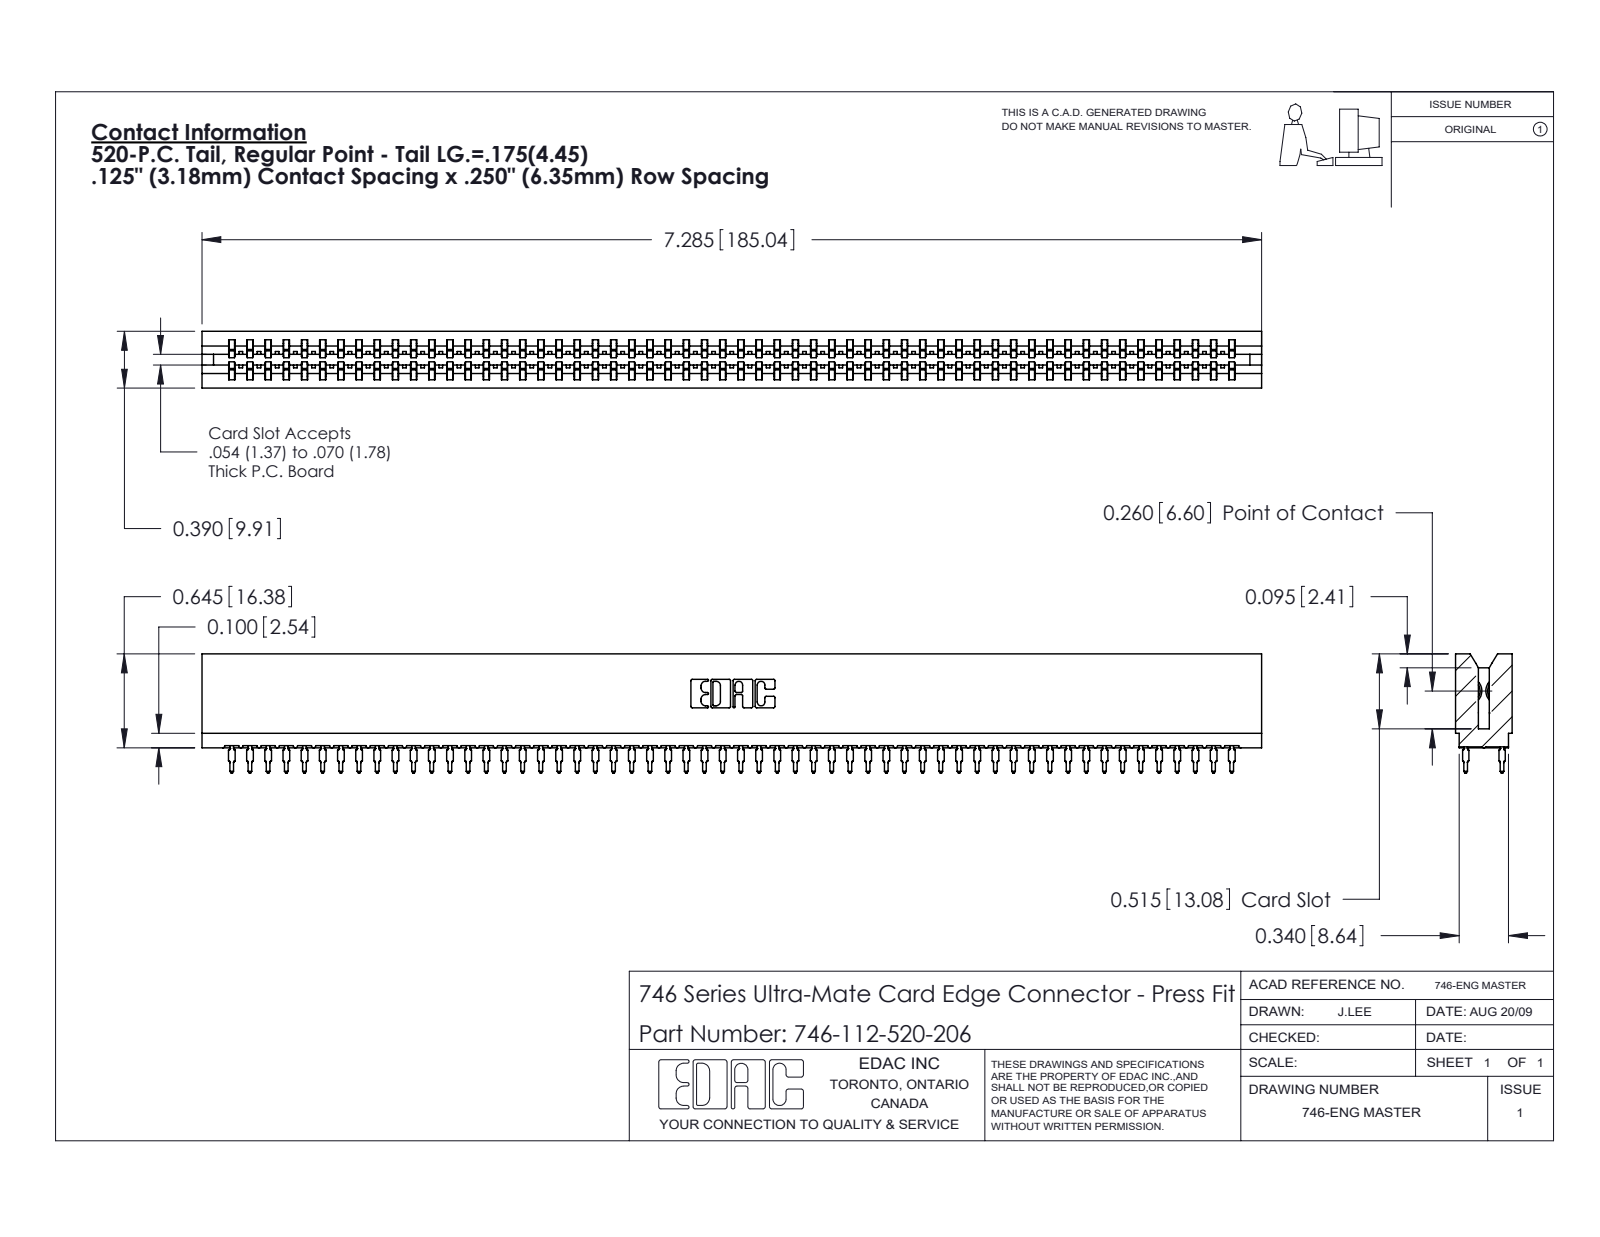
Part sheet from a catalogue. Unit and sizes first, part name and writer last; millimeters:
Units: millimetres
Overall size (bounding box): 185 × 20.8 × 9.9
Partial cylindrical surfaces — rounded edges, fillets, slot ends (radius × count): R0.5 ×224, R0.4 ×57, R0.3 ×22, R0.1 ×8, R0.3 ×8, R0.2 ×6, R0.8 ×6, R0.7 ×3
Main face-to-face distances: 1.4, 8.5, 9.9, 6.4, 0.6, 7.8, 7, 2.1, 4.4, 4
Volume: 19 630 mm³ · Surface area: 31 300 mm²
Bodies: 113 solids, 10122 faces (5208 planar, 2002 cylindrical, 2912 other)
Part name (STEP PRODUCT): 746-292-001_520; 746 Part_.515 Slot Depth - 06; 746-112-520-206
STEP written by: SolidWorks 2020 (CONFIG_CONTROL_DESIGN)
